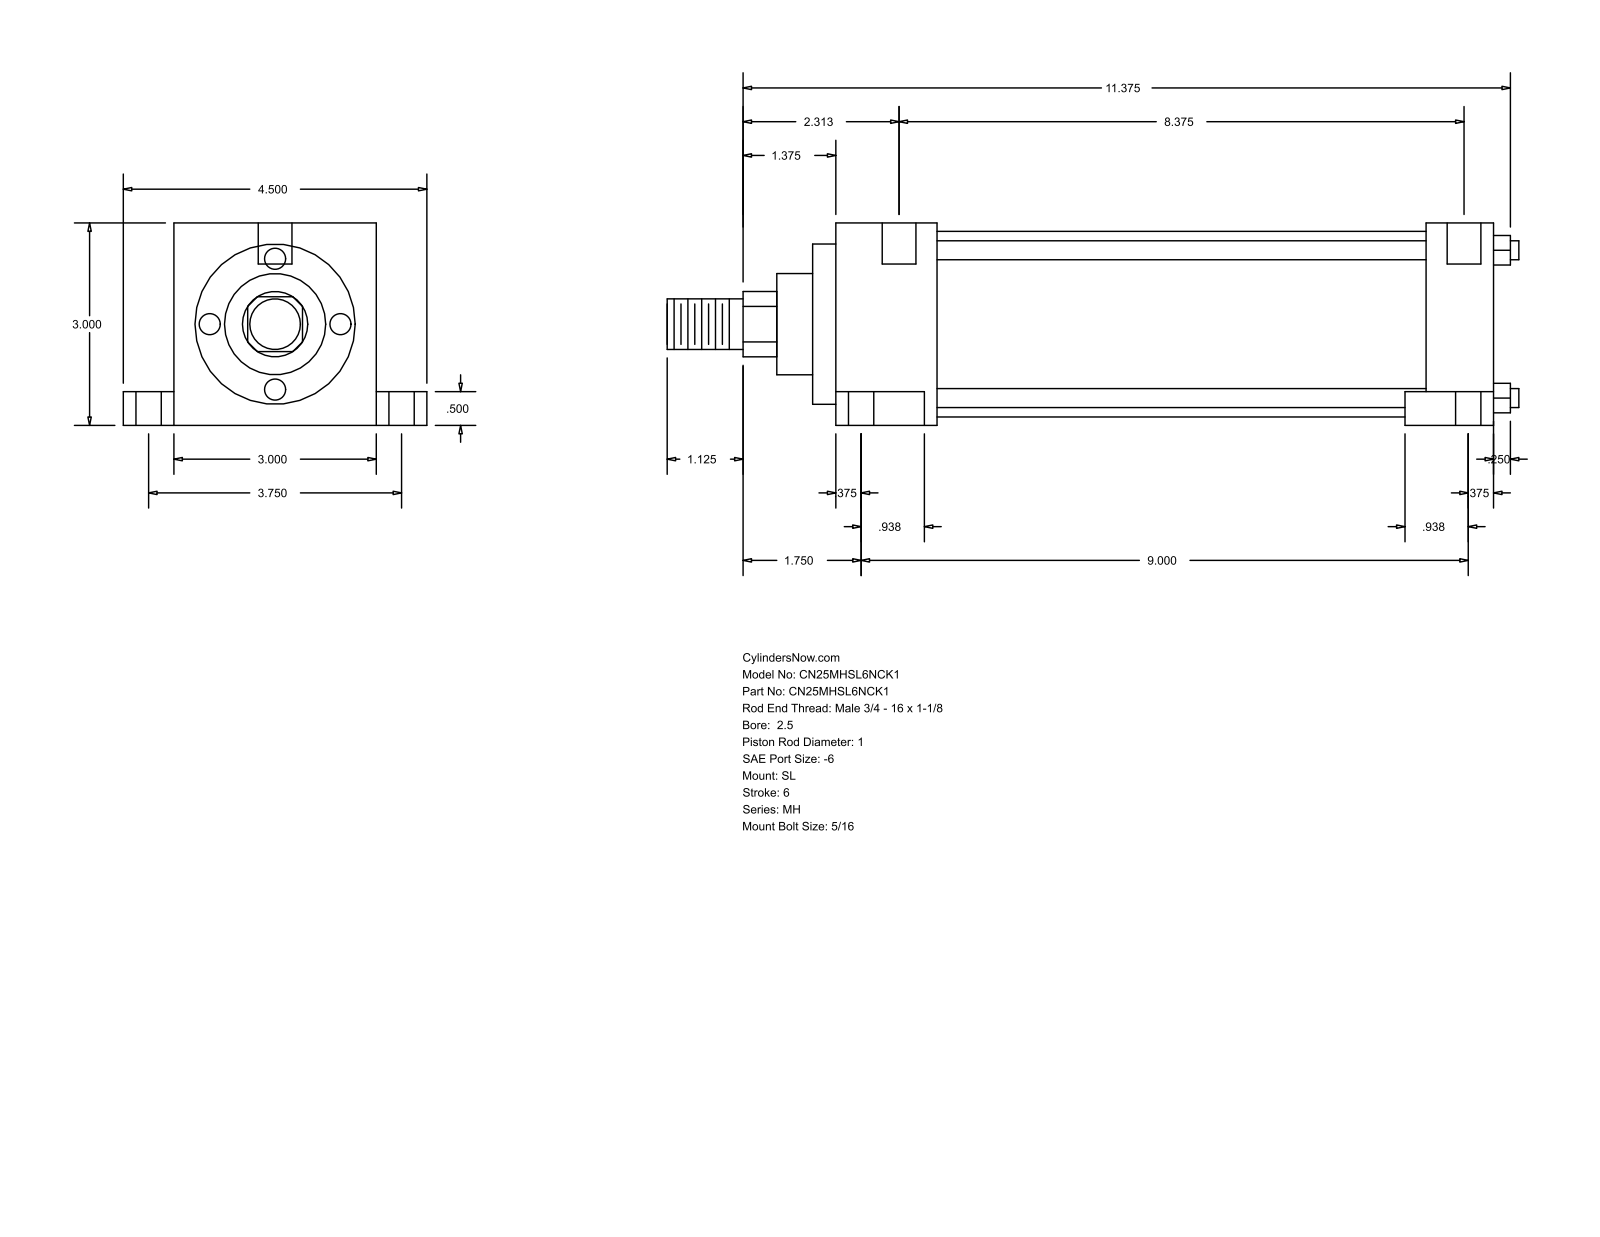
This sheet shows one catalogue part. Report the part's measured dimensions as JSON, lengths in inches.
{"part_name": "MH_SL__0250_1", "step_written_by": "GSSL Pune (CONFIG_CONTROL_DESIGN)", "units": "inches", "bodies": {"solids": 0, "faces": 86, "planar": 61, "cylindrical": 25, "other": 0}, "overall_size": [12.625, 4.5, 3], "round_holes": [[0.219, 2], [0.375, 2], [0.625, 2], [0.5, 1]], "round_bosses_or_shafts": [[0.281, 4], [2.75, 1], [2.375, 1], [1.5, 1], [1, 1], [0.75, 1]], "partial_cylinders_radius": [[0.484, 1]], "face_to_face_distances": [3, 1, 9.094, 10.094, 0.5, 2.5, 0.75, 3.75, 0.531, 9.625], "hole_center_spacings": [1.876, 0.125, 3.75]}
